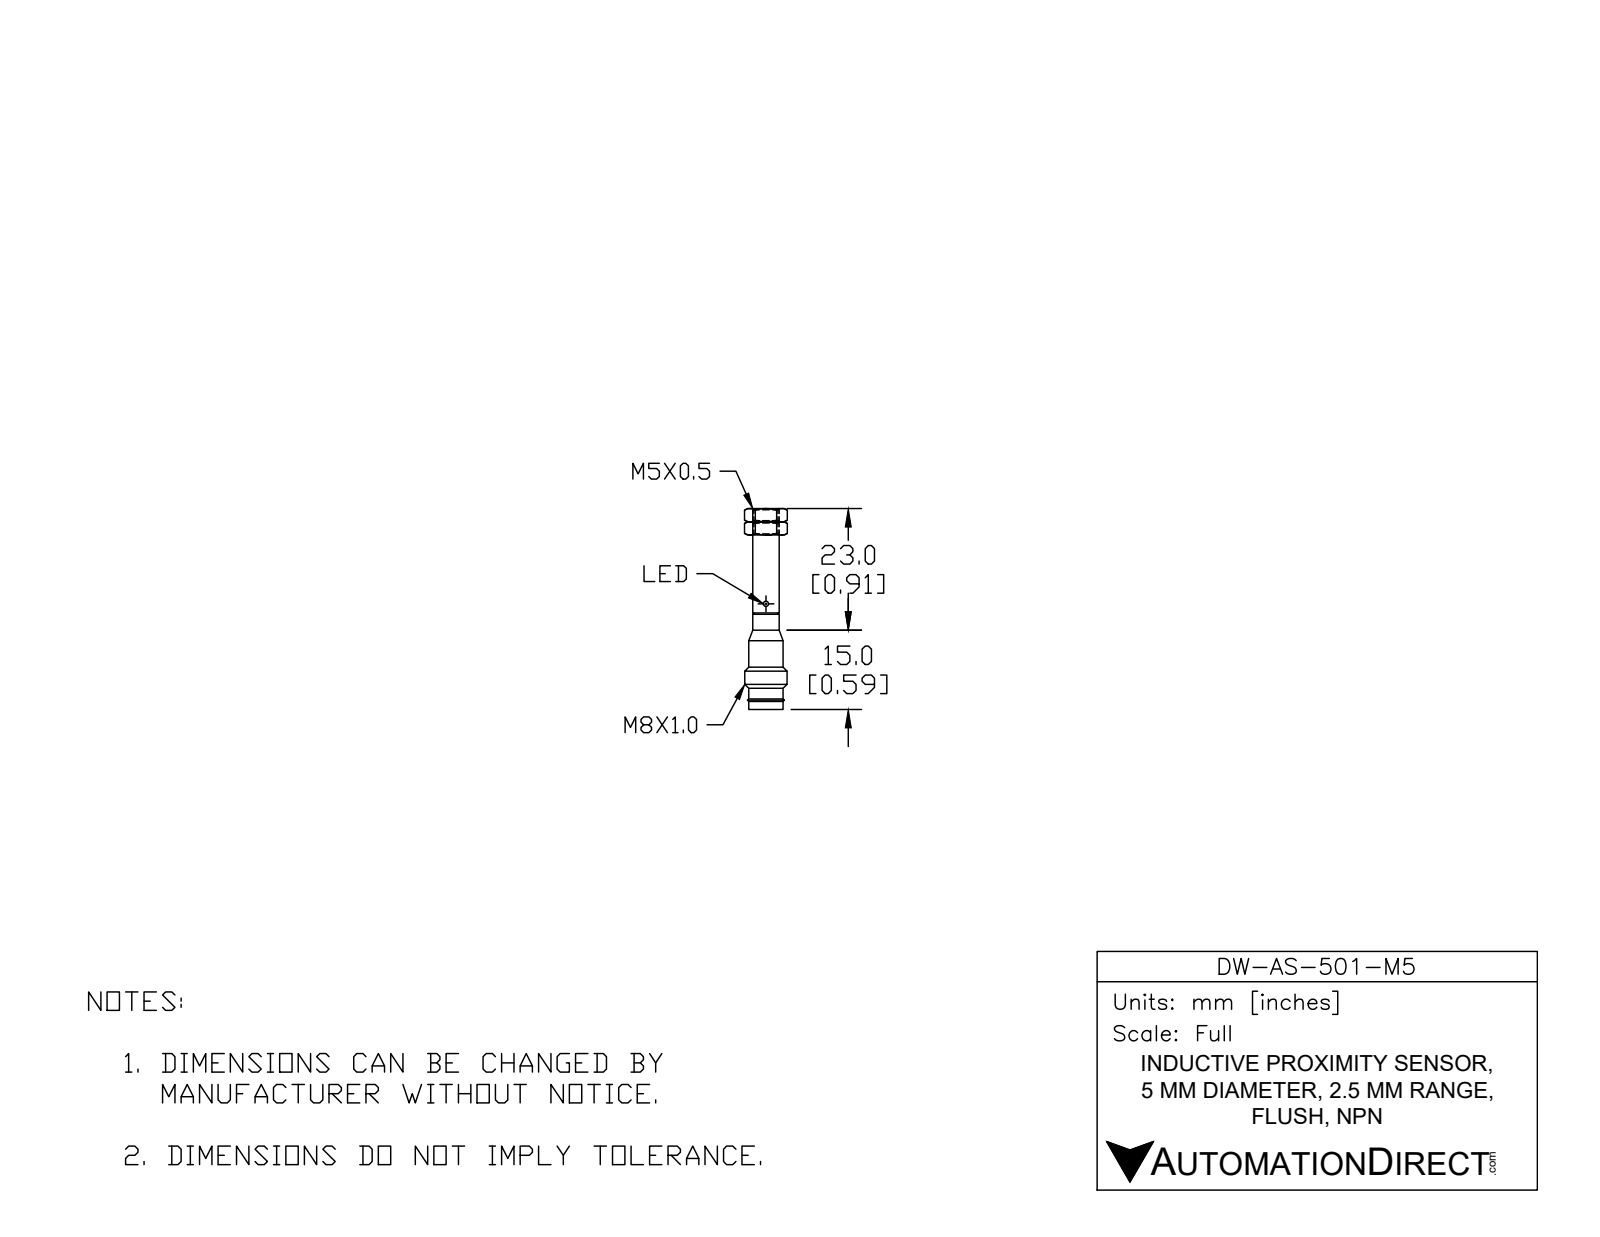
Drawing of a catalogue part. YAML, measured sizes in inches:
part_name: "DW-AS-501-M5"
step_written_by: "SolidWorks 2017 (AUTOMOTIVE_DESIGN)"
units: inches
bodies: {solids: 4, faces: 42, planar: 11, cylindrical: 15, other: 16}
overall_size: [1.496, 0.315, 0.315]
volume: 0.026
surface_area: 2.173
round_holes:
  - {diameter: 0.059, count: 1}
  - {diameter: 0.14, count: 1}
  - {diameter: 0.217, count: 1}
  - {diameter: 0.228, count: 1}
round_bosses_or_shafts:
  - {diameter: 0.039, count: 3}
  - {diameter: 0.315, count: 1}
  - {diameter: 0.272, count: 1}
  - {diameter: 0.256, count: 1}
  - {diameter: 0.228, count: 1}
  - {diameter: 0.197, count: 1}
  - {diameter: 0.132, count: 1}
face_to_face_distances: [0.03, 1.269, 1.299, 1.267, 1.297, 0.051, 0.049, 1.218, 1.248, 0.047]
